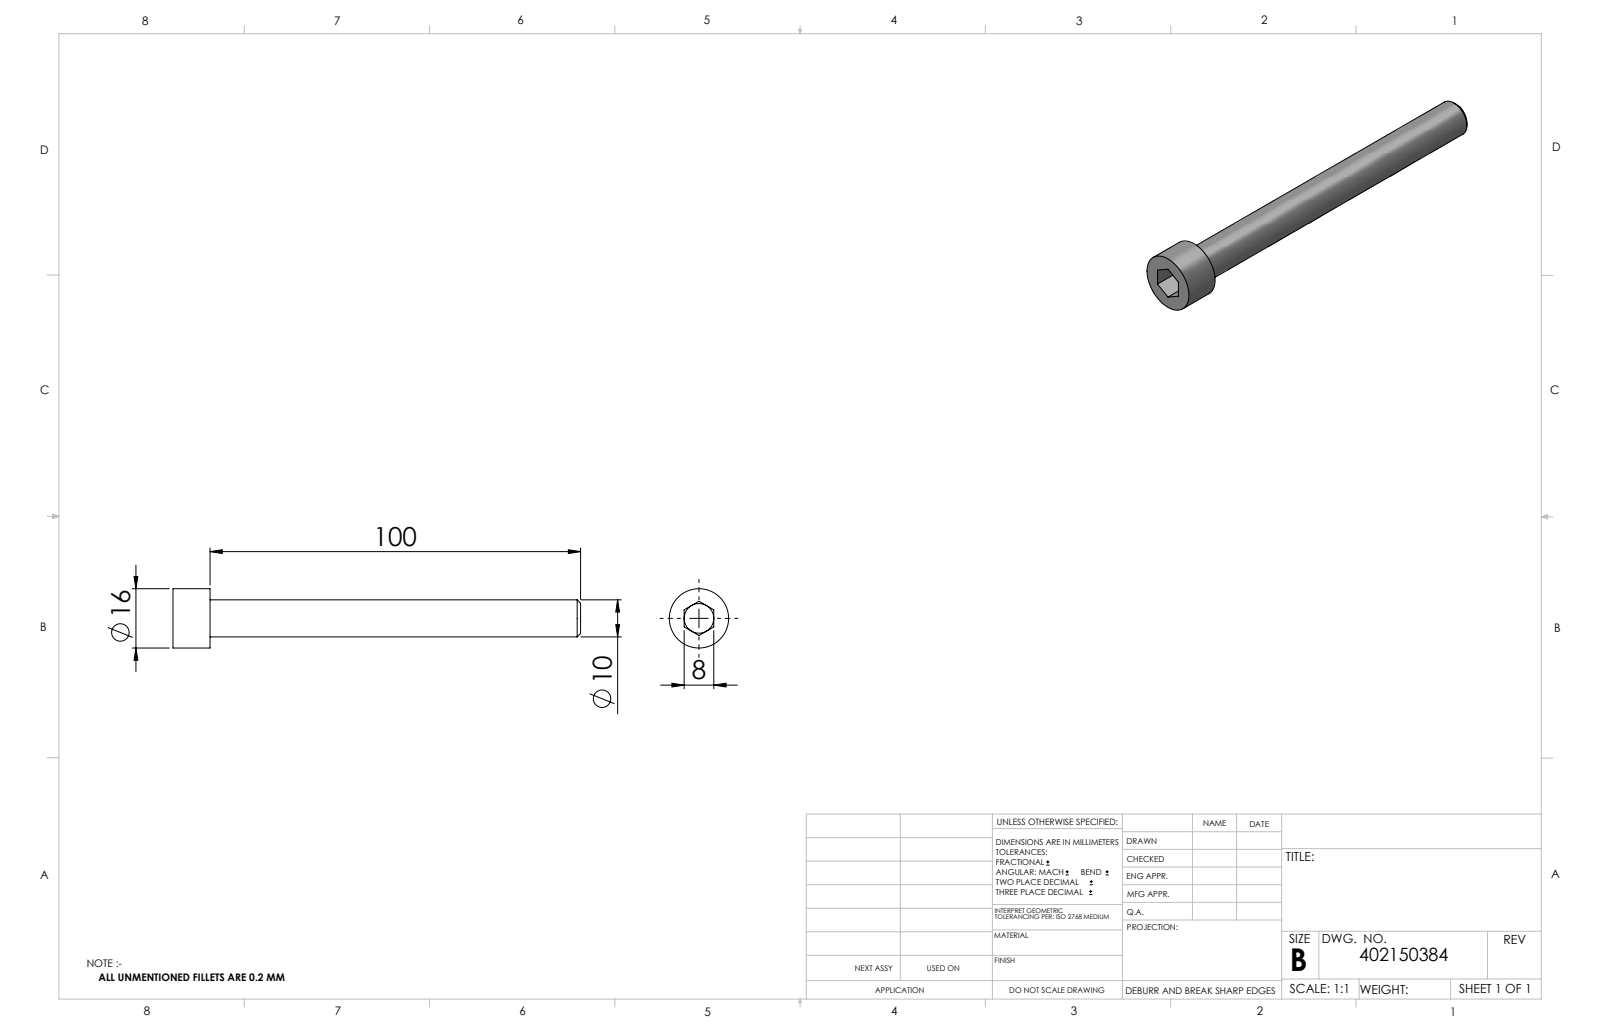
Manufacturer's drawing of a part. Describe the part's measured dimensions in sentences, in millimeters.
The part is named "402150384_c_1". Its 3-D file was written by "SolidWorks 2014 (CONFIG_CONTROL_DESIGN)". It is 1 solid with 23 faces: 15 planar, 4 cylindrical and 4 other. Overall it measures 110 by 16 by 16 millimeters. Its volume is 9 481 cubic millimeters and its surface area 4 202 square millimeters. Round bosses or shafts: 1 of diameter 16, 1 of diameter 10. The main face-to-face distances are 10, 8, 110, 100, 6, 4, 104.
